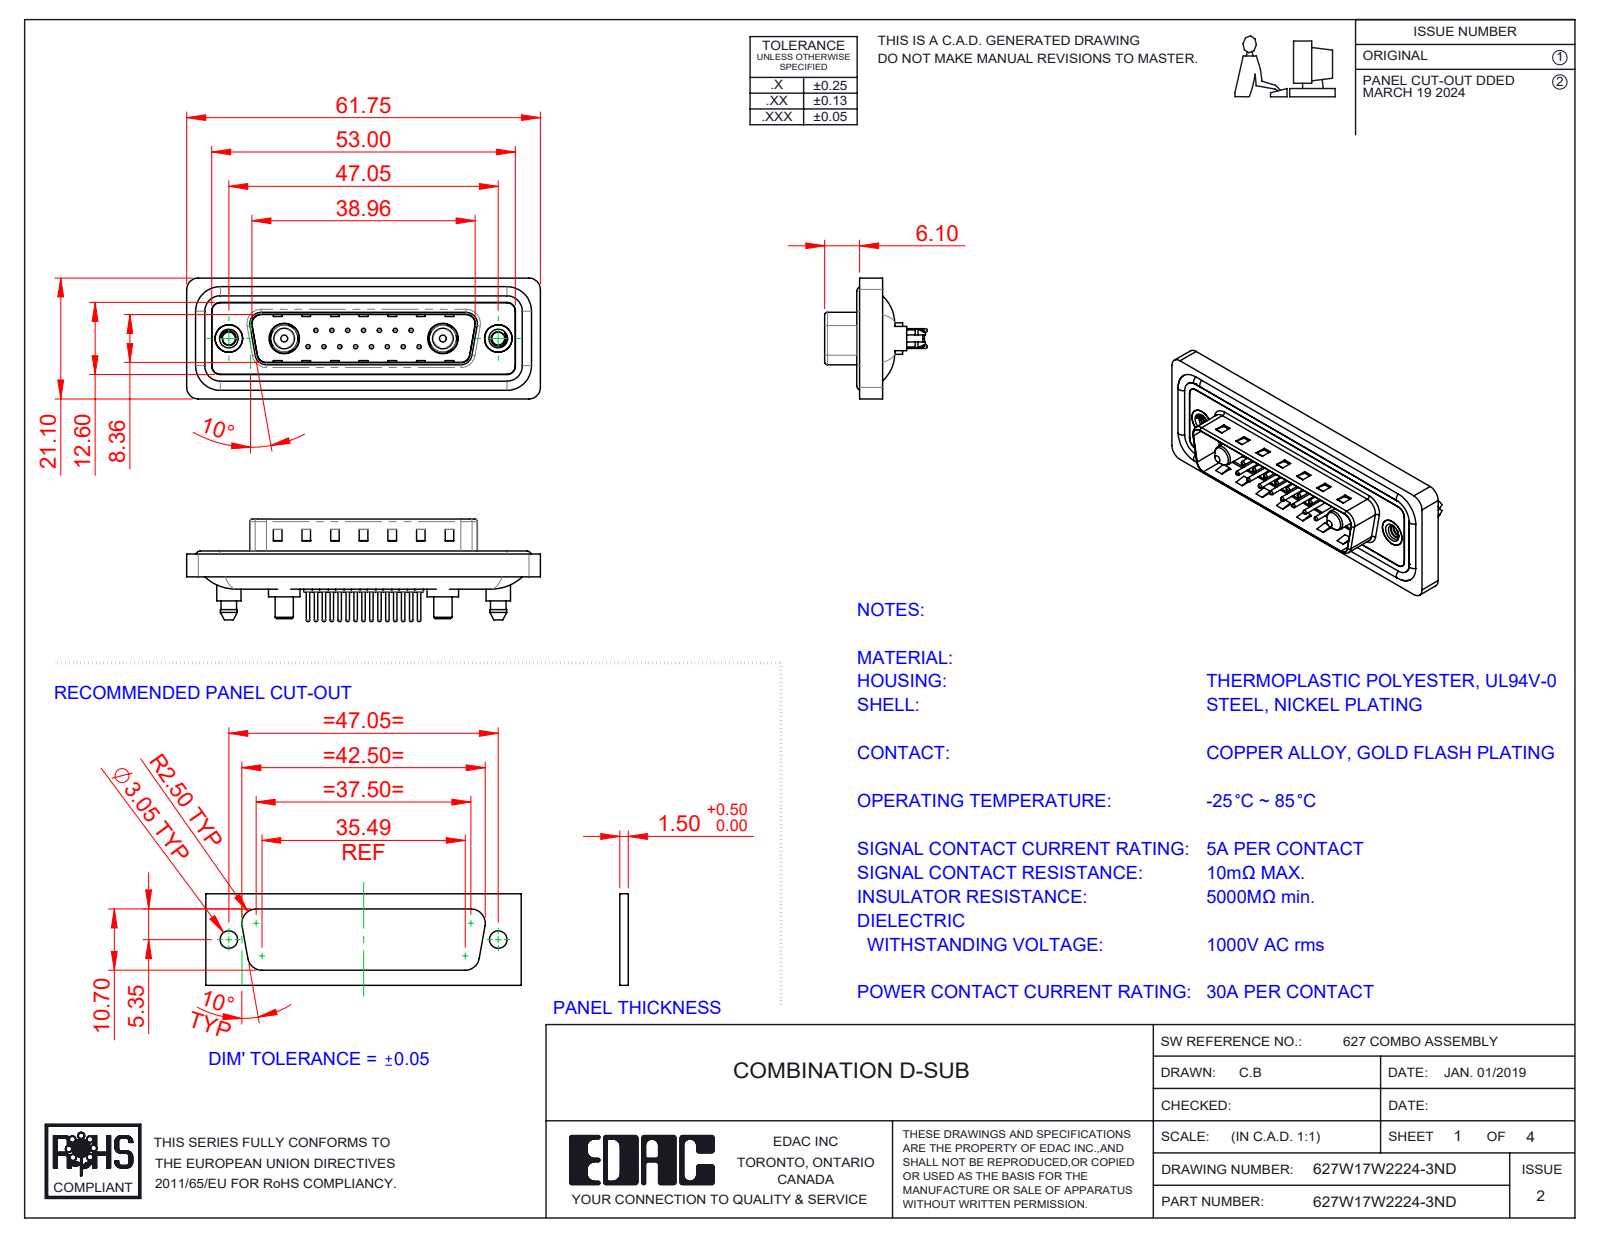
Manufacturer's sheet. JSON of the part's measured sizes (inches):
{"part_name": "627Combo Threaded Boardlock_D; Power Pin_30A S; 627W17W2224-3ND; 627Combo Threaded Boardlock_5 (+6 more)", "step_written_by": "SolidWorks 2023 (CONFIG_CONTROL_DESIGN)", "units": "inches", "bodies": {"solids": 26, "faces": 1174, "planar": 350, "cylindrical": 476, "other": 348}, "overall_size": [2.431, 0.831, 0.705], "volume_in3": 0.452, "surface_area_in2": 19, "round_holes": [[0.03, 15], [0.063, 15], [0.079, 15], [0.089, 2], [0.157, 2], [0.189, 2], [0.191, 2], [0.197, 2], [0.209, 2]], "round_bosses_or_shafts": [[0.059, 15], [0.024, 15], [0.063, 4], [0.217, 2], [0.213, 2], [0.205, 2], [0.193, 2], [0.187, 2]], "partial_cylinders_radius": [[0.059, 24], [0.079, 18], [0.063, 10], [0.02, 8], [0.01, 4], [0.024, 4], [0.026, 4], [0.035, 4]], "face_to_face_distances": [0.016, 0.059, 0.043, 0.063, 0.02, 0.122, 0.114, 0.032, 0.377, 0.161], "hole_center_spacings": [0.124, 0.109, 0.218, 0.327, 0.198, 0.295, 0.436, 0.198]}
